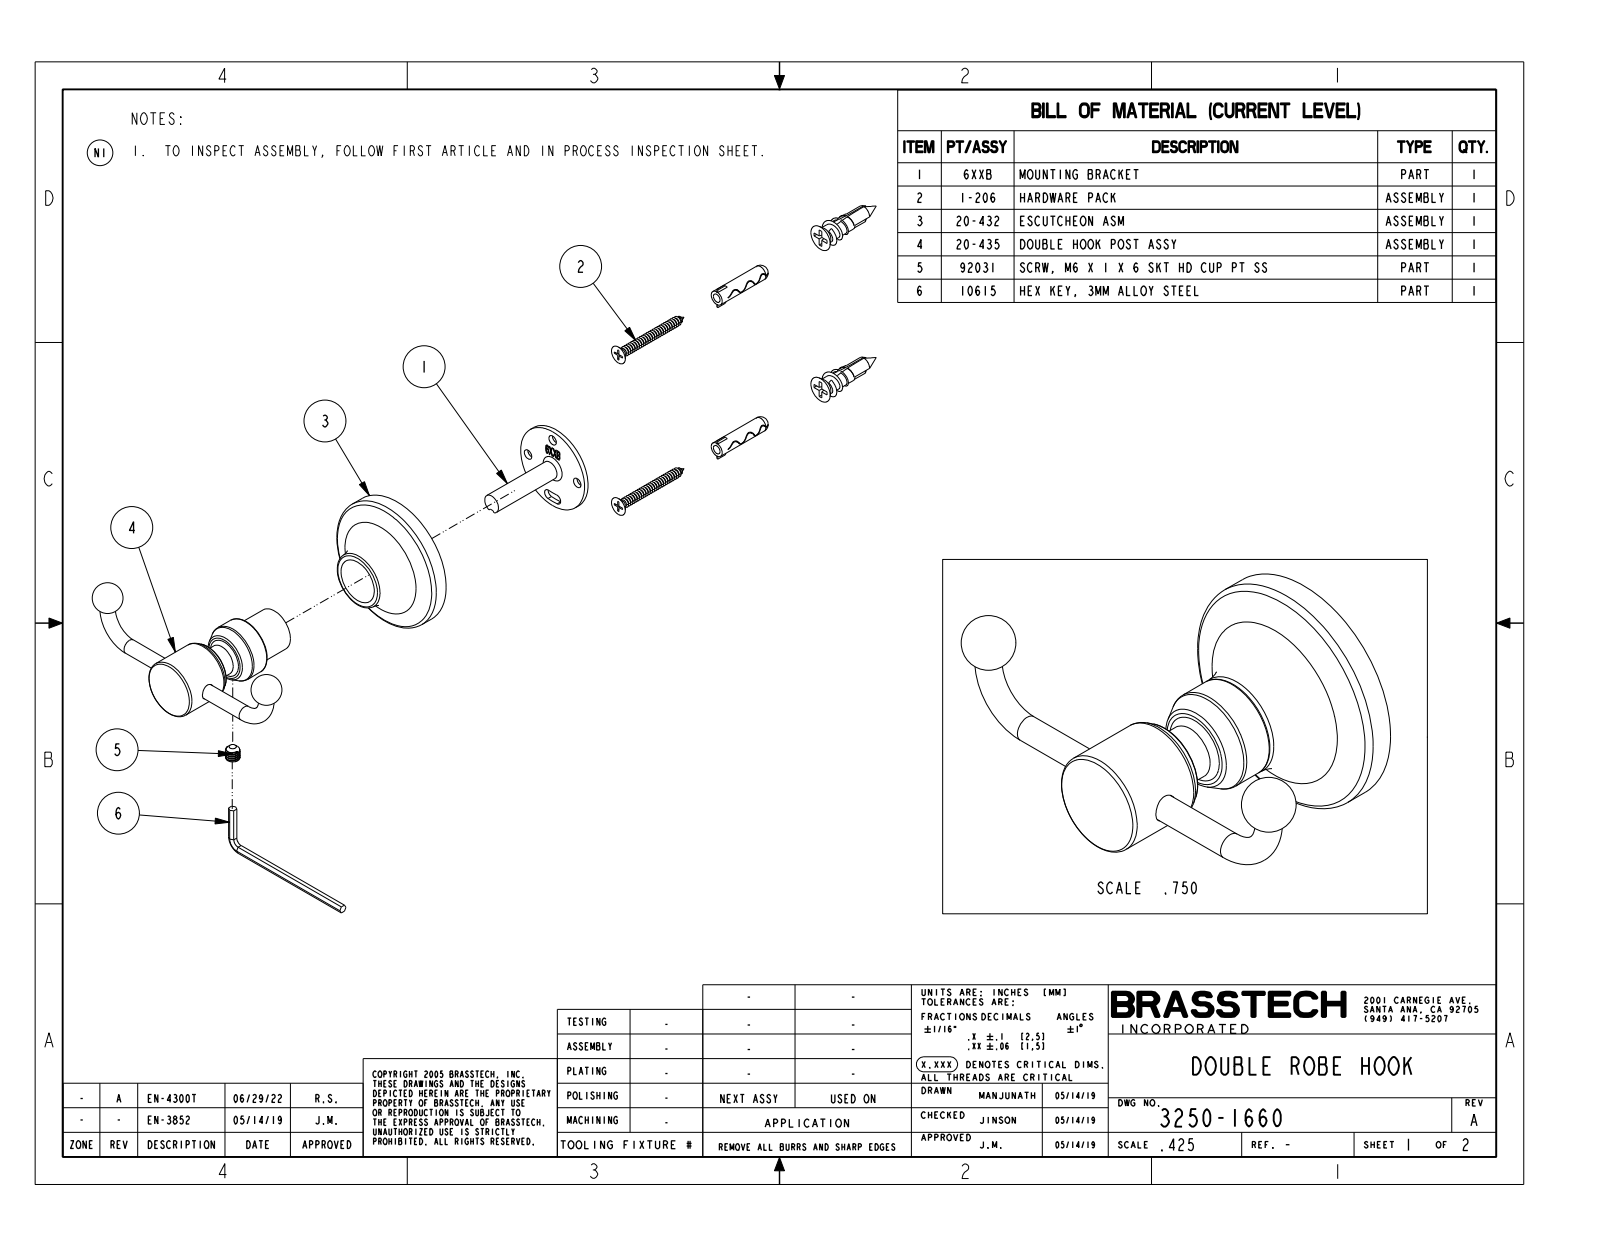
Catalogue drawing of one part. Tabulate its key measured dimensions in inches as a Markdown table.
| quantity | value |
| --- | --- |
| part name | 3250-1660 |
| STEP written by | CREO PARAMETRIC BY PTC INC, 2019352 (CONFIG_CONTROL_DESIGN) |
| units | inches |
| bodies | 1 solid, 59 faces (7 planar, 14 cylindrical, 38 other) |
| overall size | 4.133 × 2.79 × 2.25 |
| volume | 3.333 in³ |
| surface area | 20.56 in² |
| round bosses / shafts (diameter × count) | 2.25 × 1, 0.965 × 1, 0.85 × 1, 0.52 × 1, 0.25 × 1 |
| main face-to-face distances | 1.79, 0.91, 0.88, 1.415, 0.505, 0.375, 0.9, 0.515, 0.89 |
